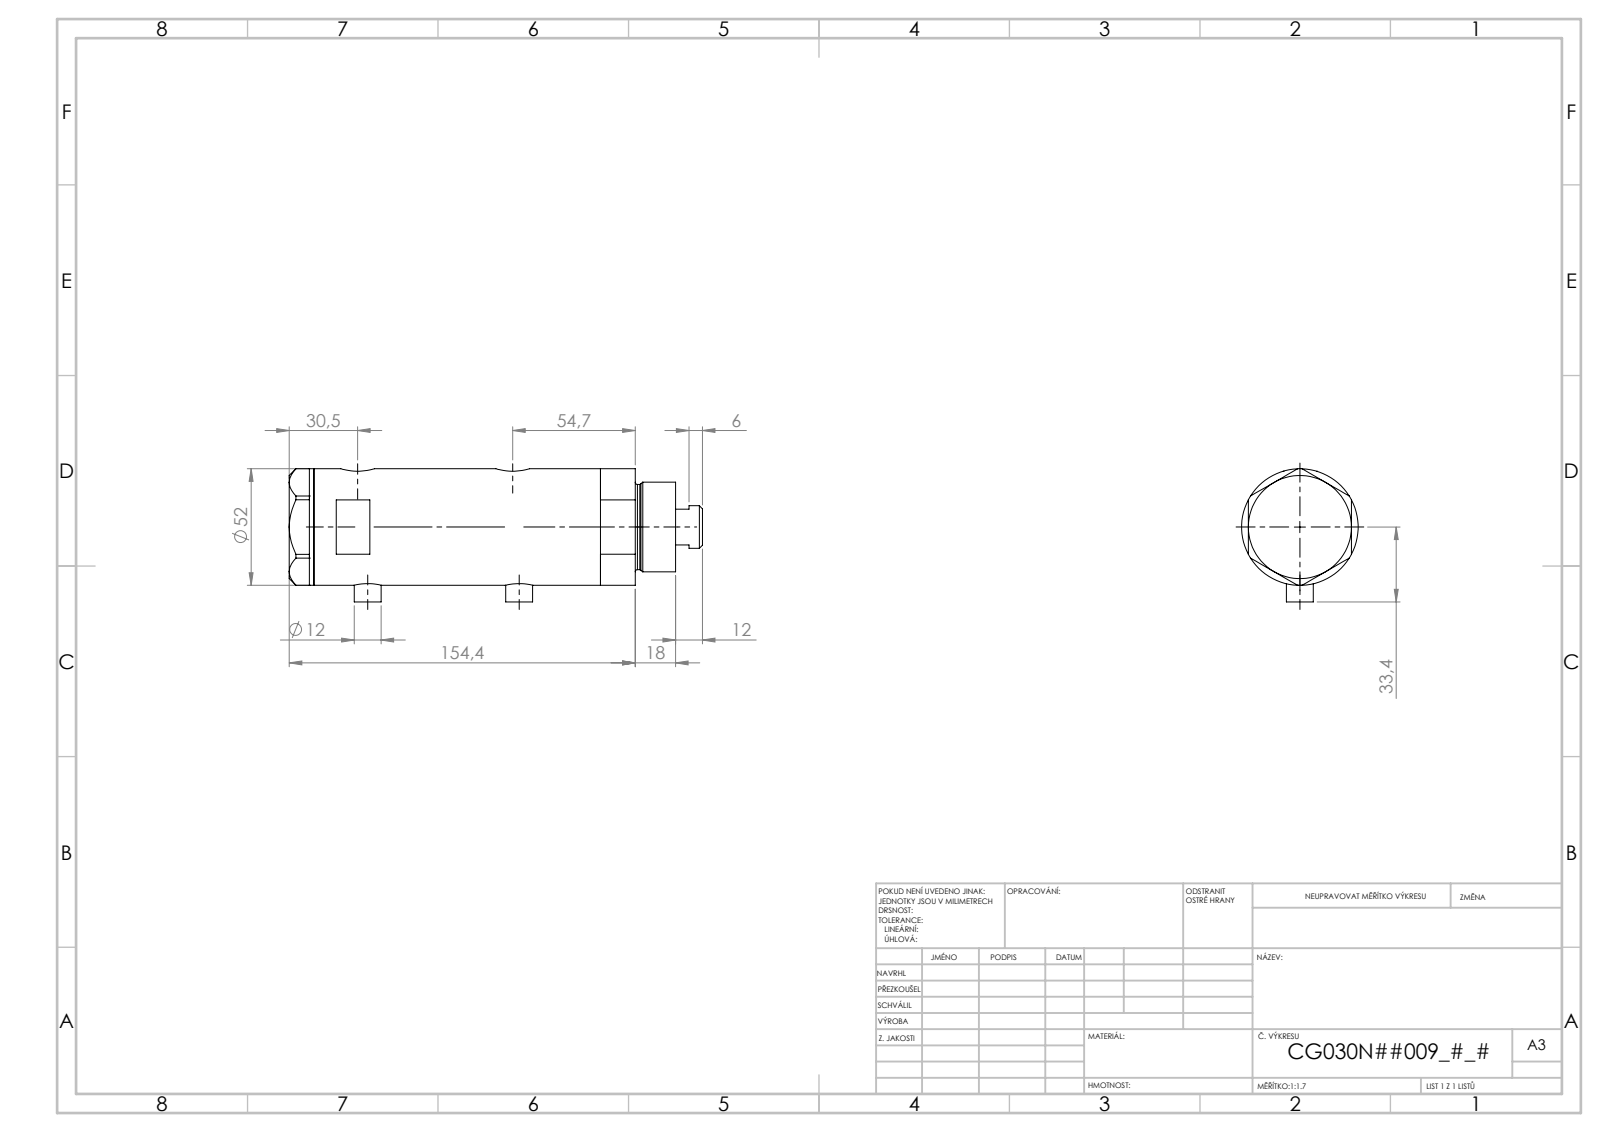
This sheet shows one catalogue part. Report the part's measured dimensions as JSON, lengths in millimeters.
{"part_name": "V270CG_MIDDLE; V270CG_VC; V270CG_FRONT; V270CG_BACK", "step_written_by": "SolidWorks 2019 (CONFIG_CONTROL_DESIGN)", "units": "millimeters", "bodies": {"solids": 4, "faces": 140, "planar": 67, "cylindrical": 53, "other": 20}, "overall_size": [158.02, 53.1, 52], "volume_mm3": 283098, "surface_area_mm2": 67973, "round_holes": [[5, 2], [9.73, 2], [12.5, 2], [15, 2], [6.5, 1], [20, 1], [21.5, 1], [30, 1], [33, 1], [44, 1]], "round_bosses_or_shafts": [[12, 2], [52, 1], [40, 1], [38, 1], [19, 1]], "face_to_face_distances": [23.81, 11, 34.81, 46, 73.56, 62.56, 38.75, 109.96, 98.96, 75.15], "hole_center_spacings": [2.9, 4.5, 35.75, 38.65, 40.25, 43.15, 2.89, 2.91]}
